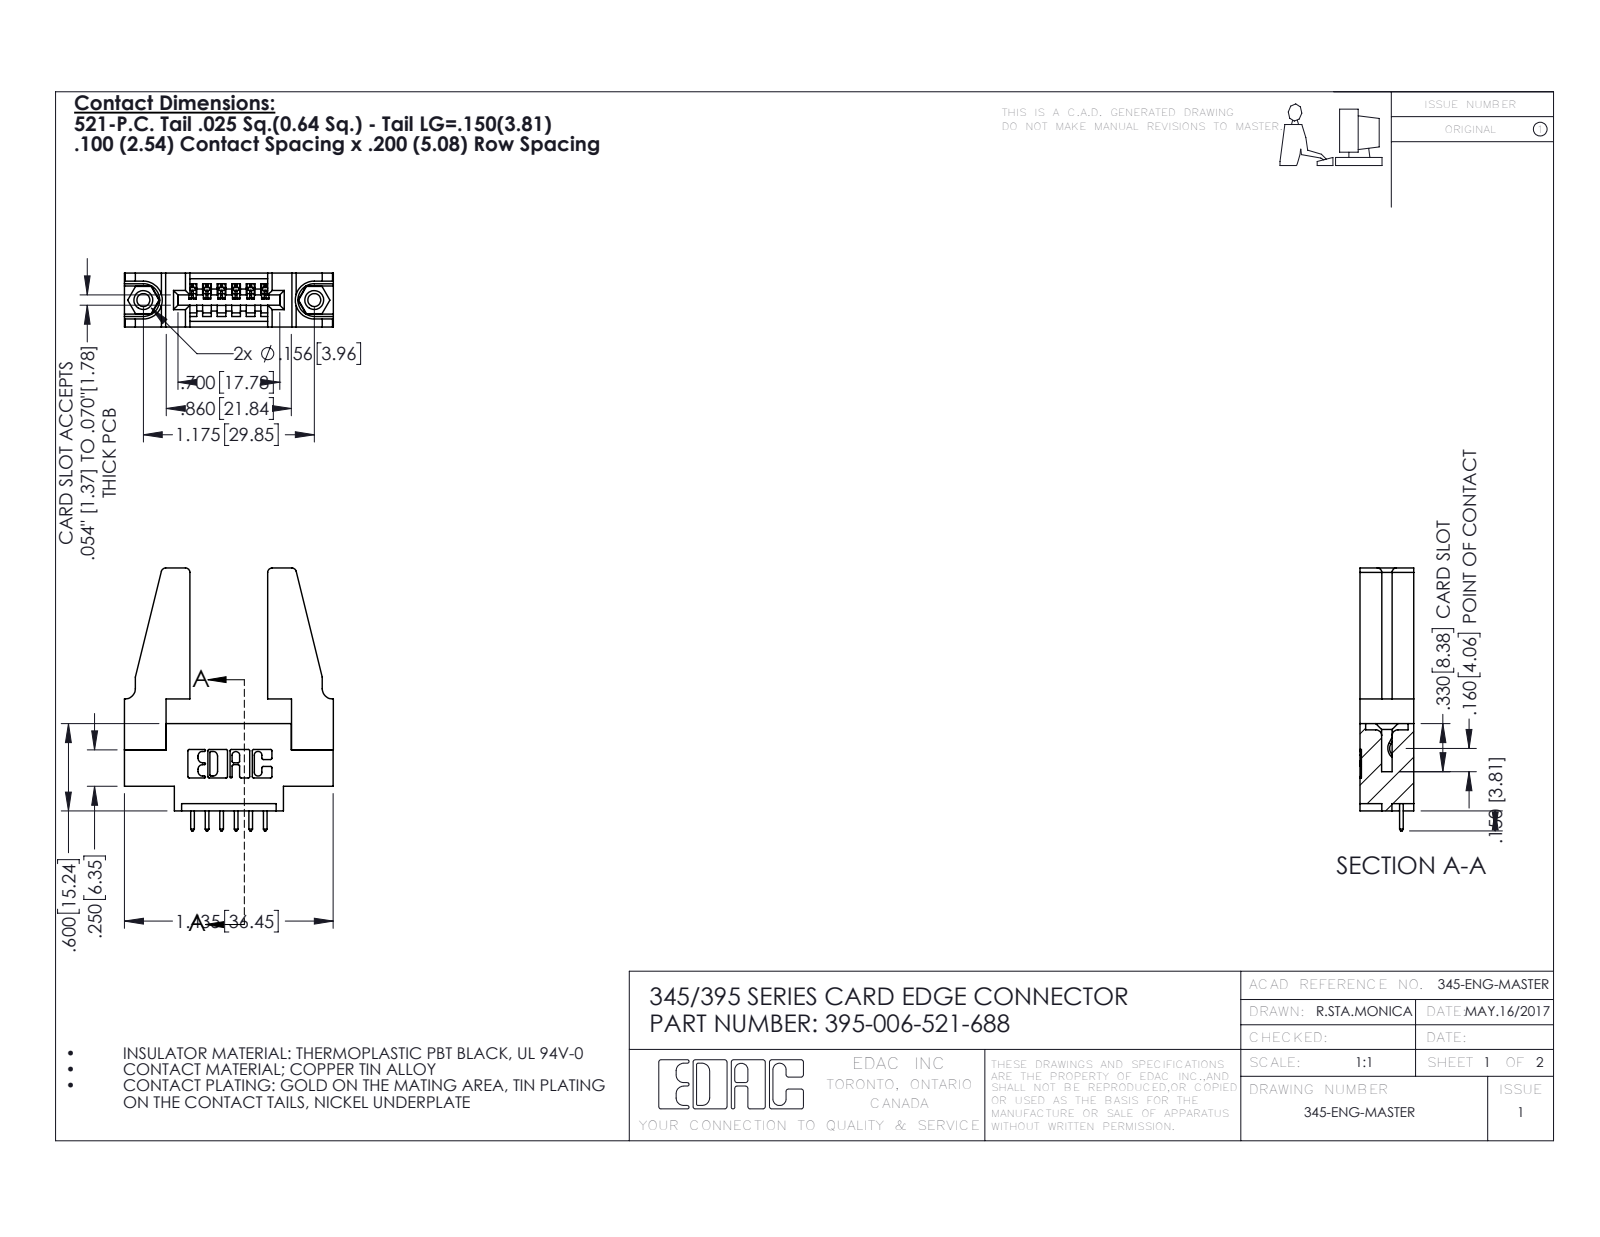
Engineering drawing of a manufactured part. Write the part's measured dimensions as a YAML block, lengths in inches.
part_name: "345 Part_0.170 Offset - 0.156 Dia-TH; 395-006-521-688; 345-250-001_345-250-001-102; 345-220-078_345-220-088 (+1 more)"
step_written_by: "SolidWorks 2016 (CONFIG_CONTROL_DESIGN)"
units: inches
bodies: {solids: 11, faces: 602, planar: 396, cylindrical: 190, other: 16}
overall_size: [1.807, 1.436, 0.37]
volume: 0.384
surface_area: 10.44
round_holes:
  - {diameter: 0.089, count: 2}
  - {diameter: 0.125, count: 2}
  - {diameter: 0.156, count: 2}
  - {diameter: 0.064, count: 1}
round_bosses_or_shafts:
  - {diameter: 0.155, count: 2}
partial_cylinders:
  - {radius: 0.01, count: 22}
  - {radius: 0.006, count: 12}
  - {radius: 0.01, count: 12}
  - {radius: 0.03, count: 8}
  - {radius: 0.007, count: 6}
  - {radius: 0.031, count: 6}
  - {radius: 0.026, count: 3}
  - {radius: 0.031, count: 2}
face_to_face_distances: [0.37, 0.072, 0.298, 0.2, 0.15, 0.148, 0.22, 0.077, 0.098, 0.272]
hole_center_spacings: [0.27, 0.946, 1.175]
